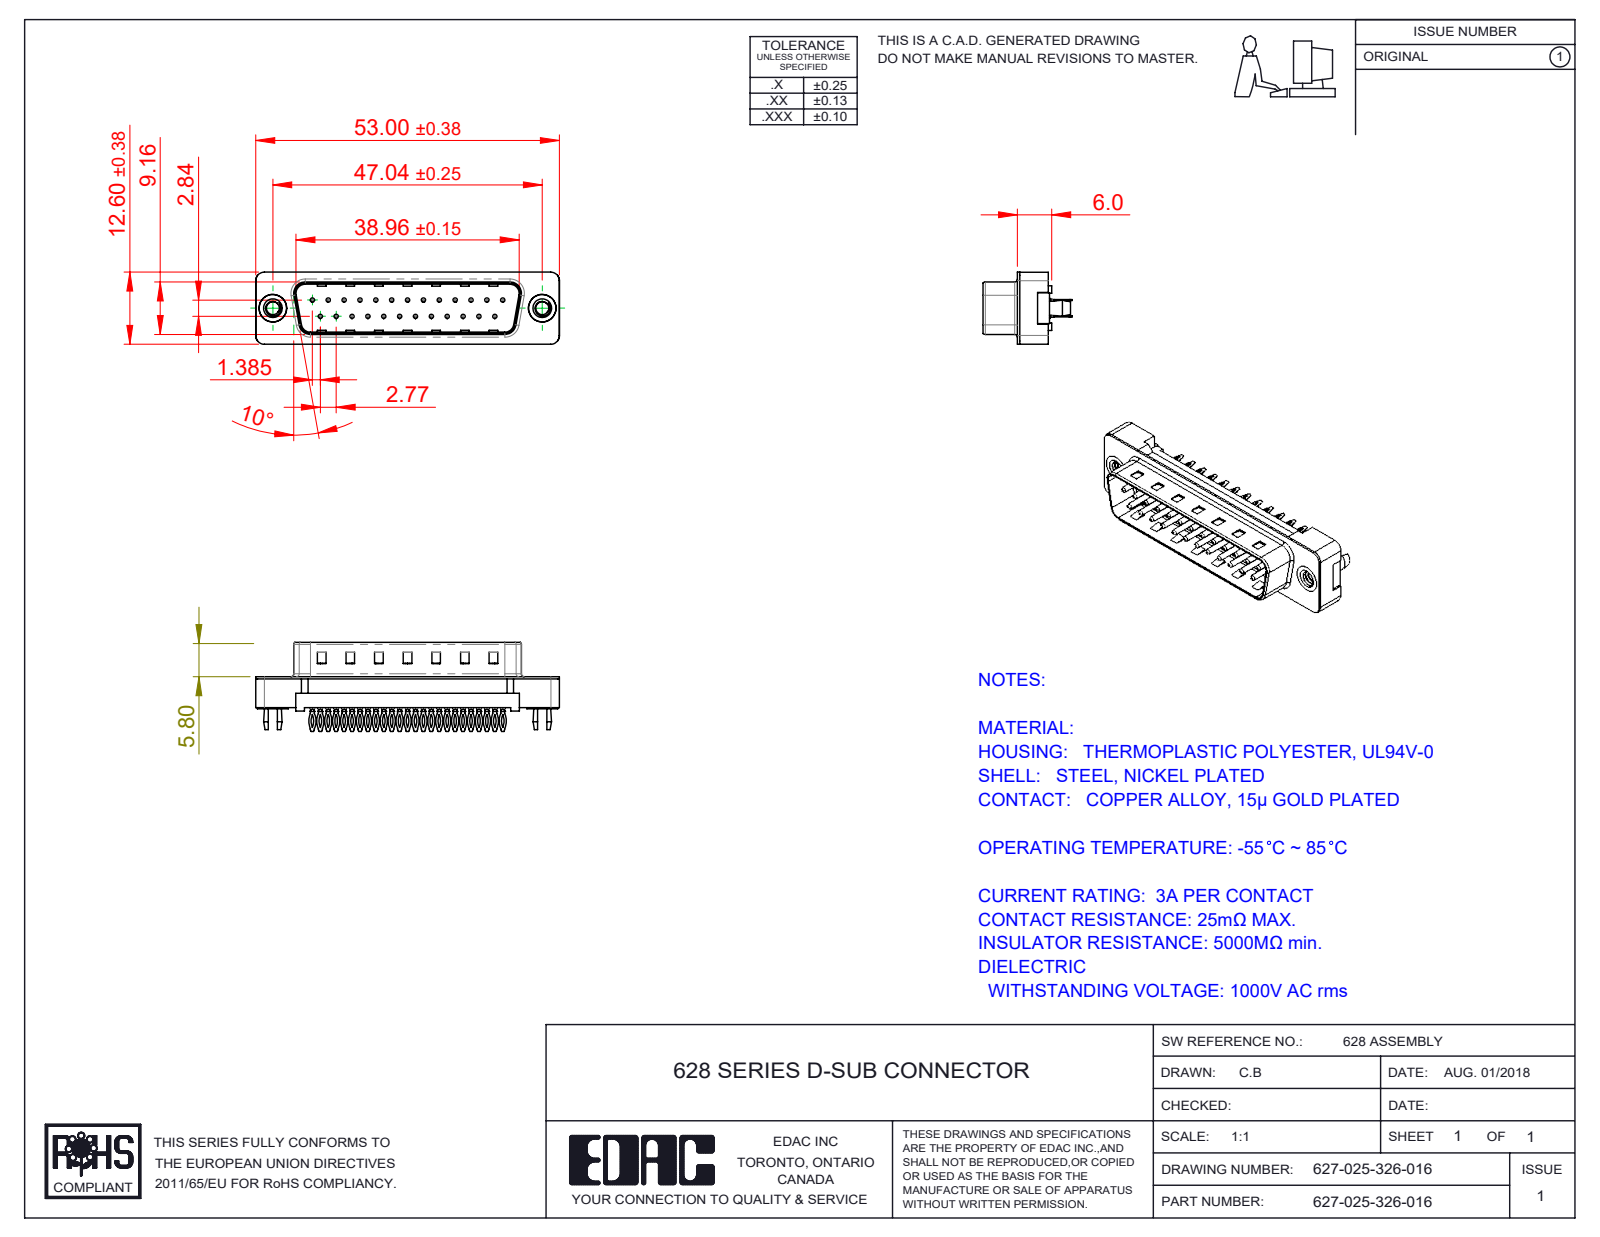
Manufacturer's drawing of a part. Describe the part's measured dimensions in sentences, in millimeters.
The part is named "627-025-326-016; 627 PB Contact Row 1_26; 627 PB Contact Row 2_26; 627 PB Shell_25 Contacts (+2 more)". Its 3-D file was written by "SolidWorks 2020 (CONFIG_CONTROL_DESIGN)". It is 29 solids with 2108 faces: 1288 planar, 598 cylindrical and 222 other. Overall it measures 53.04 by 15.55 by 12.6 millimeters. Its volume is 2 569 cubic millimeters and its surface area 5 854 square millimeters. Round holes: 25 of diameter 0.35, 25 of diameter 0.85, 2 of diameter 2.26, 2 of diameter 4, 2 of diameter 4.8, 2 of diameter 5. Round bosses or shafts: 25 of diameter 0.75, 2 of diameter 4.9. Partial cylindrical surfaces (rounded edges, fillets, slot ends): 50 of radius 0.25, 50 of radius 2.92, 50 of radius 3.33, 25 of radius 0.12, 8 of radius 0.5, 8 of radius 1.5, 4 of radius 0.9, 4 of radius 1.6. The main face-to-face distances are 0.4, 2.5, 8.76, 5.4, 2.9, 5, 8.48, 1.3, 0.68, 8.08. The hole center spacings are 3.16, 5.54, 2.77, 11.08, 8.31, 5.03, 13.85, 16.62.
